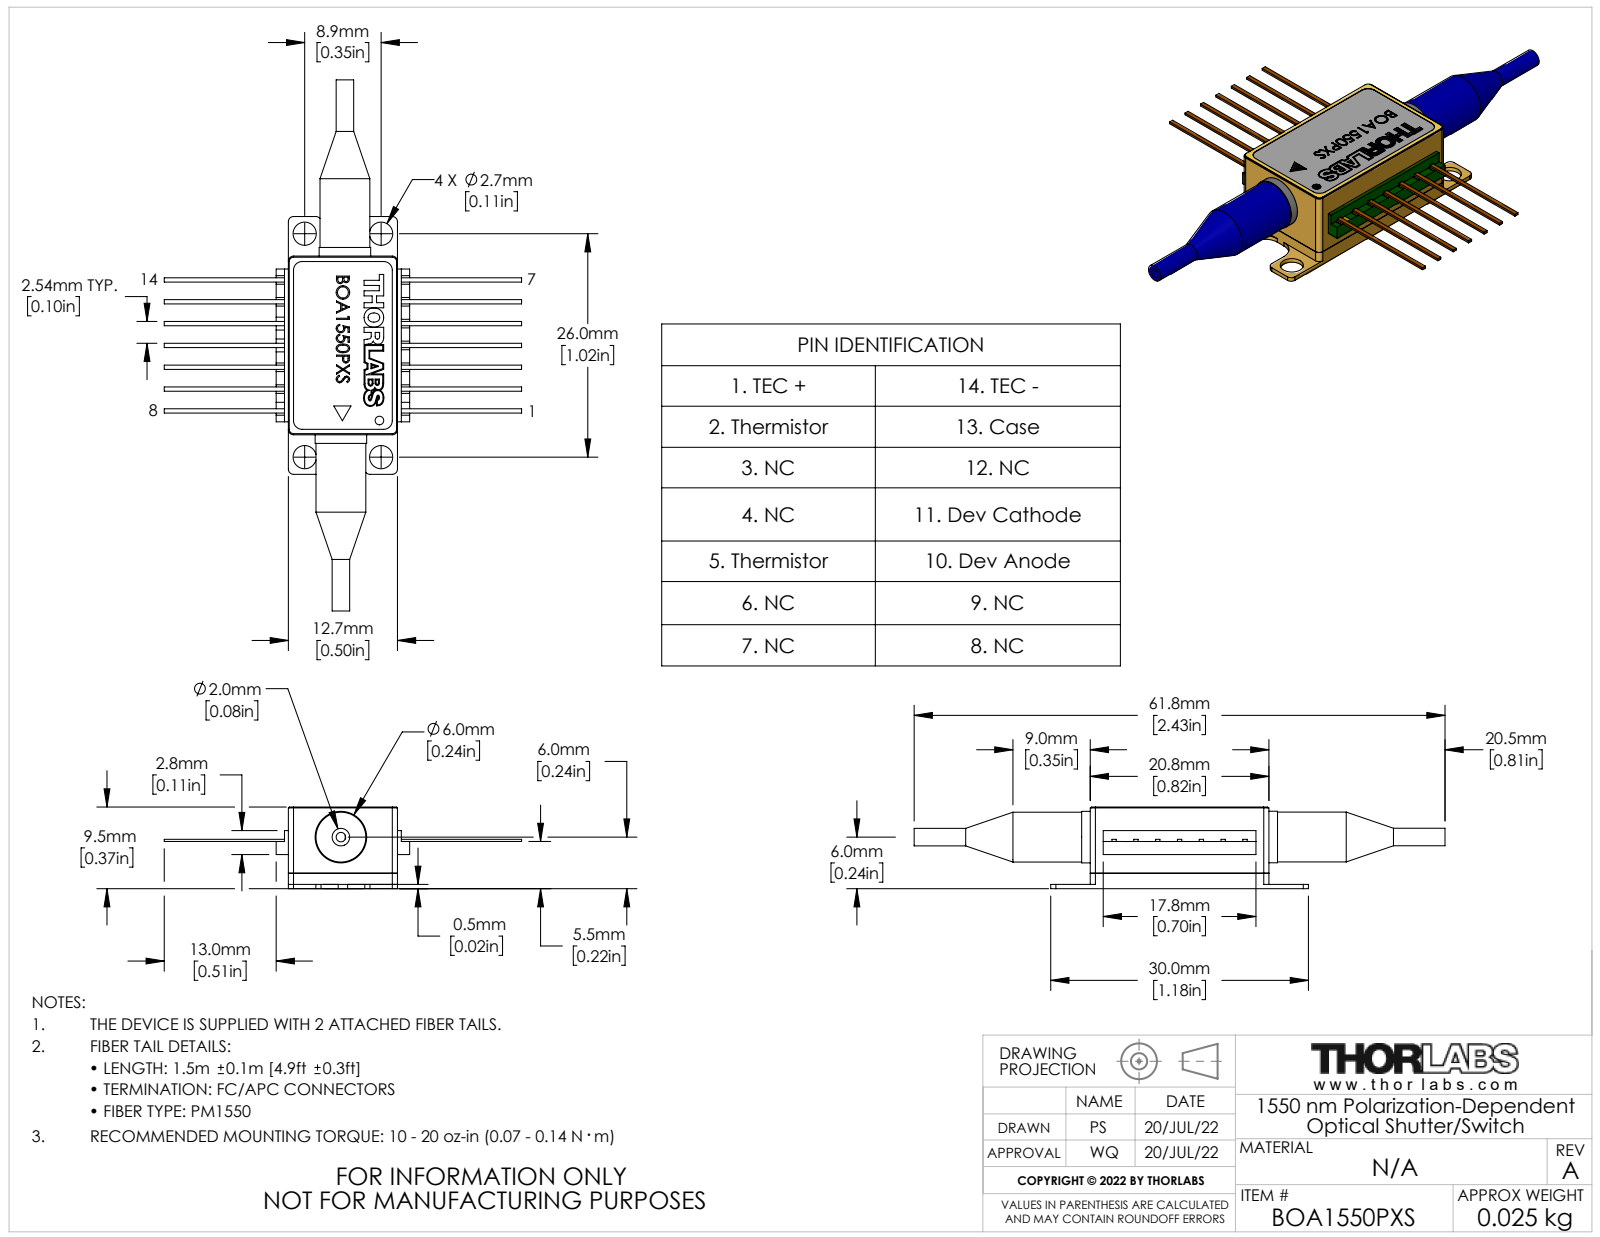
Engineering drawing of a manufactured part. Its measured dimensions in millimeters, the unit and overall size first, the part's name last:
Units: millimetres
Overall size (bounding box): 61.8 × 41.6 × 9.5
Round holes (diameter × count): ⌀2.7 ×4, ⌀1.1 ×2, ⌀2.08 ×2, ⌀3.17 ×2, ⌀3.5 ×2, ⌀4.1 ×2, ⌀1 ×1
Round bosses / shafts (diameter × count): ⌀6 ×2, ⌀5.8 ×2, ⌀3.45 ×2, ⌀3.18 ×2, ⌀2.04 ×2, ⌀2 ×2
Partial cylindrical surfaces — rounded edges, fillets, slot ends (radius × count): R1 ×16, R0.6 ×12, R0.2 ×4, R0.5 ×4, R2 ×4
Main face-to-face distances: 1, 3.7, 7.6, 3.9, 1.8, 9.49, 7.69, 3.97, 9.2, 7.4
Hole centre spacings: 8.9, 26, 27.48, 0.47, 4.26, 9.69, 21.74, 23.42
Volume: 1 669 mm³ · Surface area: 4 551 mm²
Bodies: 27 solids, 695 faces (447 planar, 102 cylindrical, 146 other)
Part name (STEP PRODUCT): QTN043856-E0W
STEP written by: SolidWorks 2018 (AUTOMOTIVE_DESIGN)
